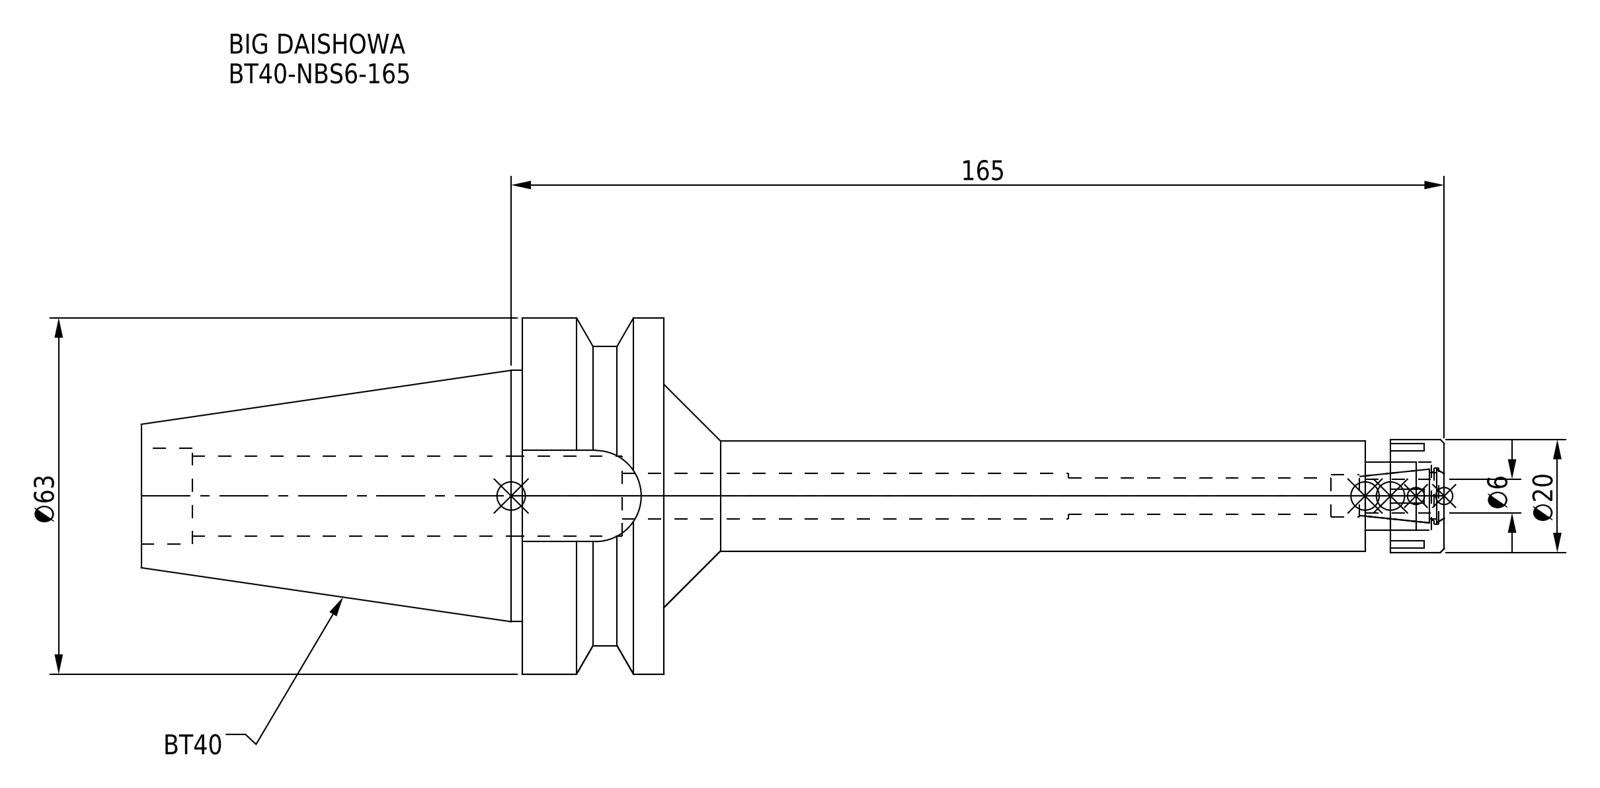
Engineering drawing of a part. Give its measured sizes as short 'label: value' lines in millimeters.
name: BT40-NBS6-165.stp; BT40-NBS6-165-FreeParts; BT40NB06165-060_ASM.stp; DXF_TEMP_ASSY_ASM_4_ASM.stp (+3 more)
written by: SolidWorks 2019 (CONFIG_CONTROL_DESIGN)
unit: mm
bodies: 2 solids, 93 faces (45 planar, 34 cylindrical, 14 other)
size: 230.4 × 63 × 63
volume: 158 065 mm³; area: 35 082 mm²
holes: 1× ⌀6.4, 1× ⌀7.5, 1× ⌀8, 1× ⌀8.5, 1× ⌀10, 1× ⌀12, 1× ⌀14.2, 1× ⌀17
bosses: 1× ⌀63, 1× ⌀53, 1× ⌀44.45, 1× ⌀20, 1× ⌀19.5
rounds: 1× R8.05
face distances: 25, 45, 92.4, 67.4, 216.4, 4.5, 138, 163, 230.4, 14
